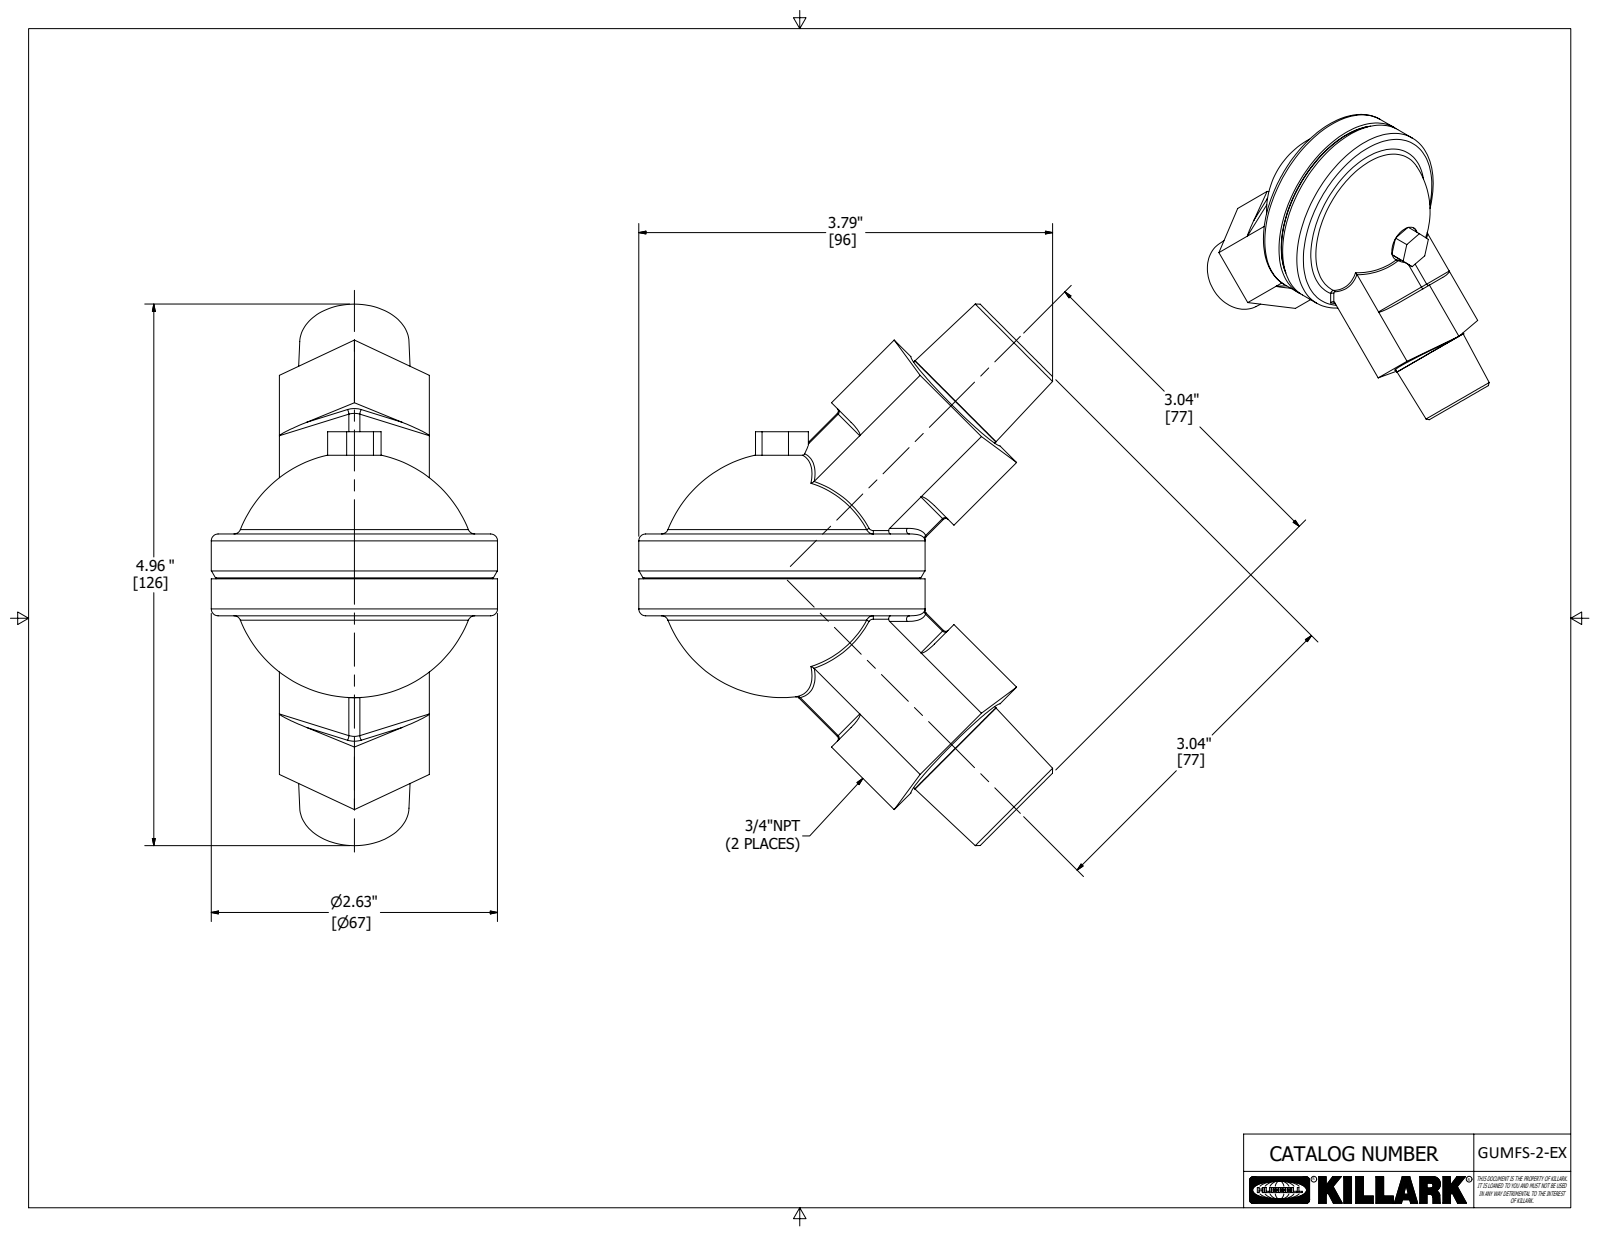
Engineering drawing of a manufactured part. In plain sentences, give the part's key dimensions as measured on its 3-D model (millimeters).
The part is named "GUMFS-2; 0078418M; 0078419M; 06857AAEB (+1 more)". Its 3-D file was written by "Autodesk Inventor 2020 (AUTOMOTIVE_DESIGN)". It is 5 solids with 210 faces: 76 planar, 41 cylindrical and 93 other. Overall it measures 126.1 by 96.4 by 66.7 millimeters. Its volume is 123 700 cubic millimeters and its surface area 54 830 square millimeters. Round holes: 2 of diameter 20.1, 2 of diameter 21.2, 2 of diameter 22.2, 1 of diameter 6.4, 1 of diameter 9.5, 1 of diameter 12.7, 1 of diameter 41.3. Round bosses or shafts: 2 of diameter 26.7, 1 of diameter 66.7, 1 of diameter 15.9, 1 of diameter 9.5, 1 of diameter 8, 1 of diameter 7.9, 1 of diameter 6.1. Partial cylindrical surfaces (rounded edges, fillets, slot ends): 16 of radius 0.8, 4 of radius 3.2. The main face-to-face distances are 34.9, 34.9, 8.8, 10.2, 19.1, 32.5, 1.4, 10.4, 1.6, 8.6.
